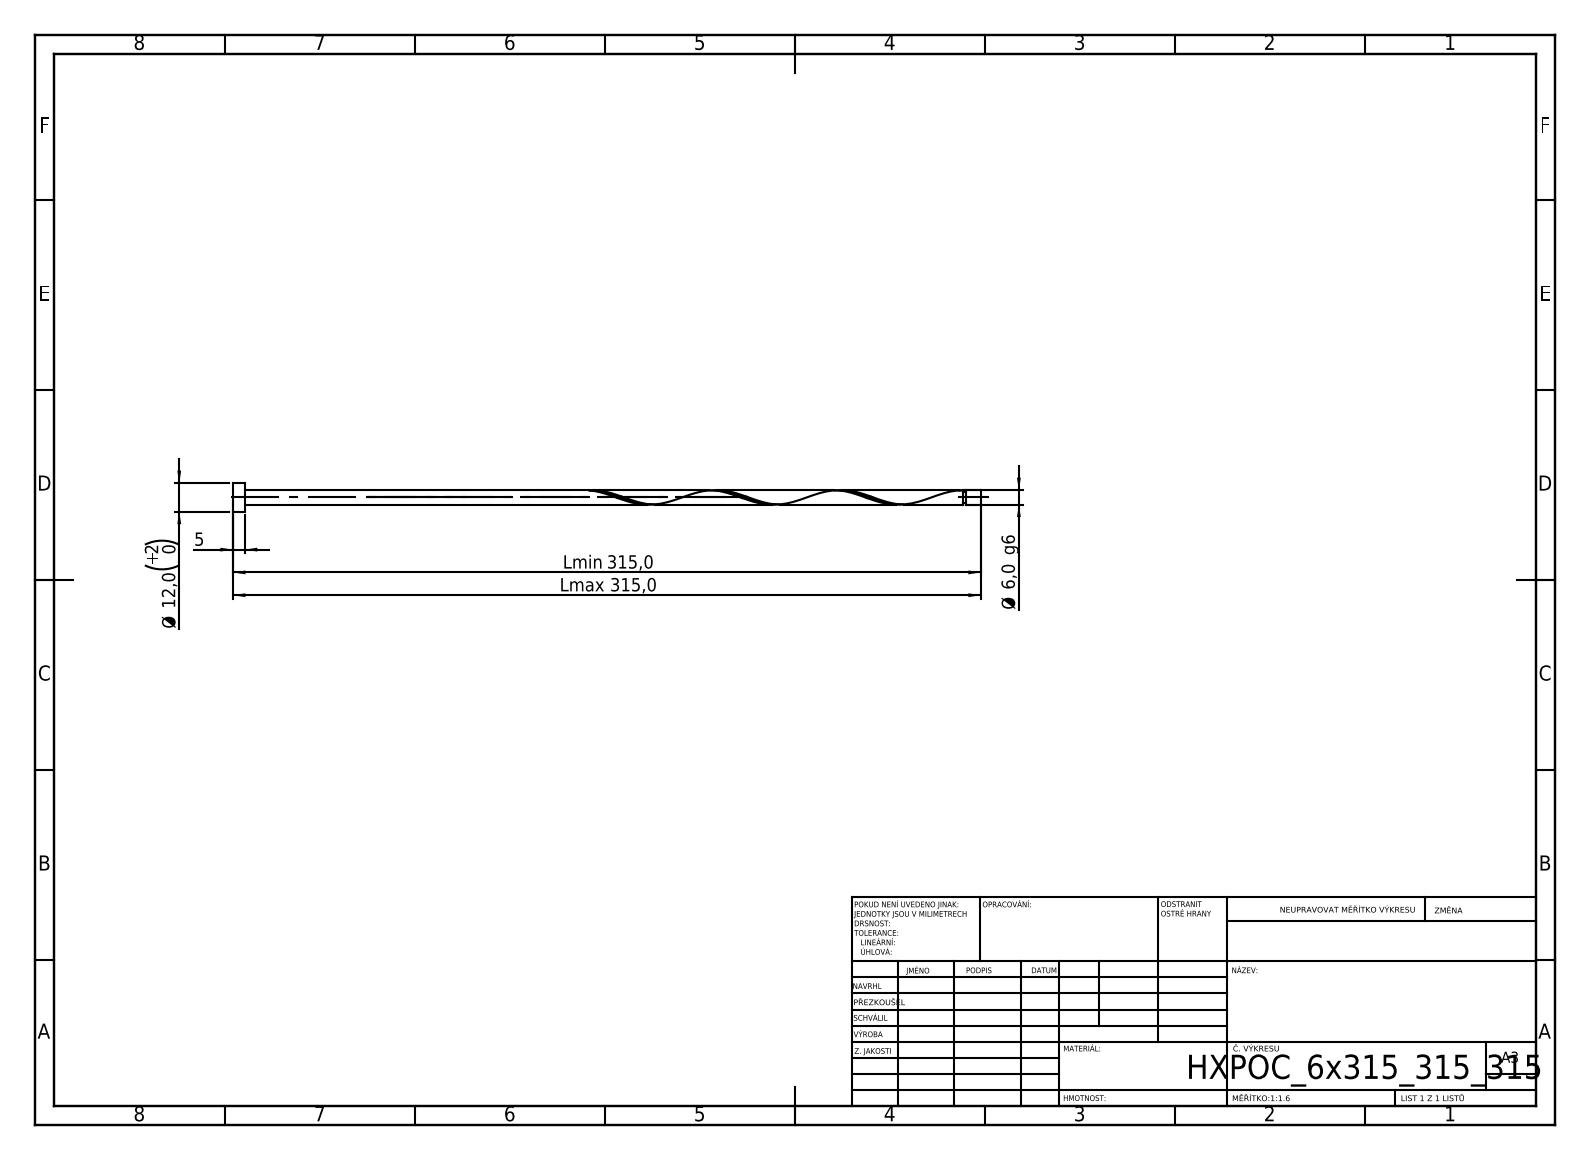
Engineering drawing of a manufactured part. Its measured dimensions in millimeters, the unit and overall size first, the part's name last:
Units: millimetres
Overall size (bounding box): 315 × 12 × 12
Round bosses / shafts (diameter × count): ⌀12 ×1, ⌀6 ×1, ⌀4.8 ×1
Main face-to-face distances: 5, 315, 310, 308.54, 303.54, 6.46, 307.34, 302.34, 1.2, 7.66
Volume: 9 233 mm³ · Surface area: 6 371 mm²
Bodies: 1 solid, 21 faces (6 planar, 14 cylindrical, 1 other)
STEP written by: SolidWorks 2019 (CONFIG_CONTROL_DESIGN)
